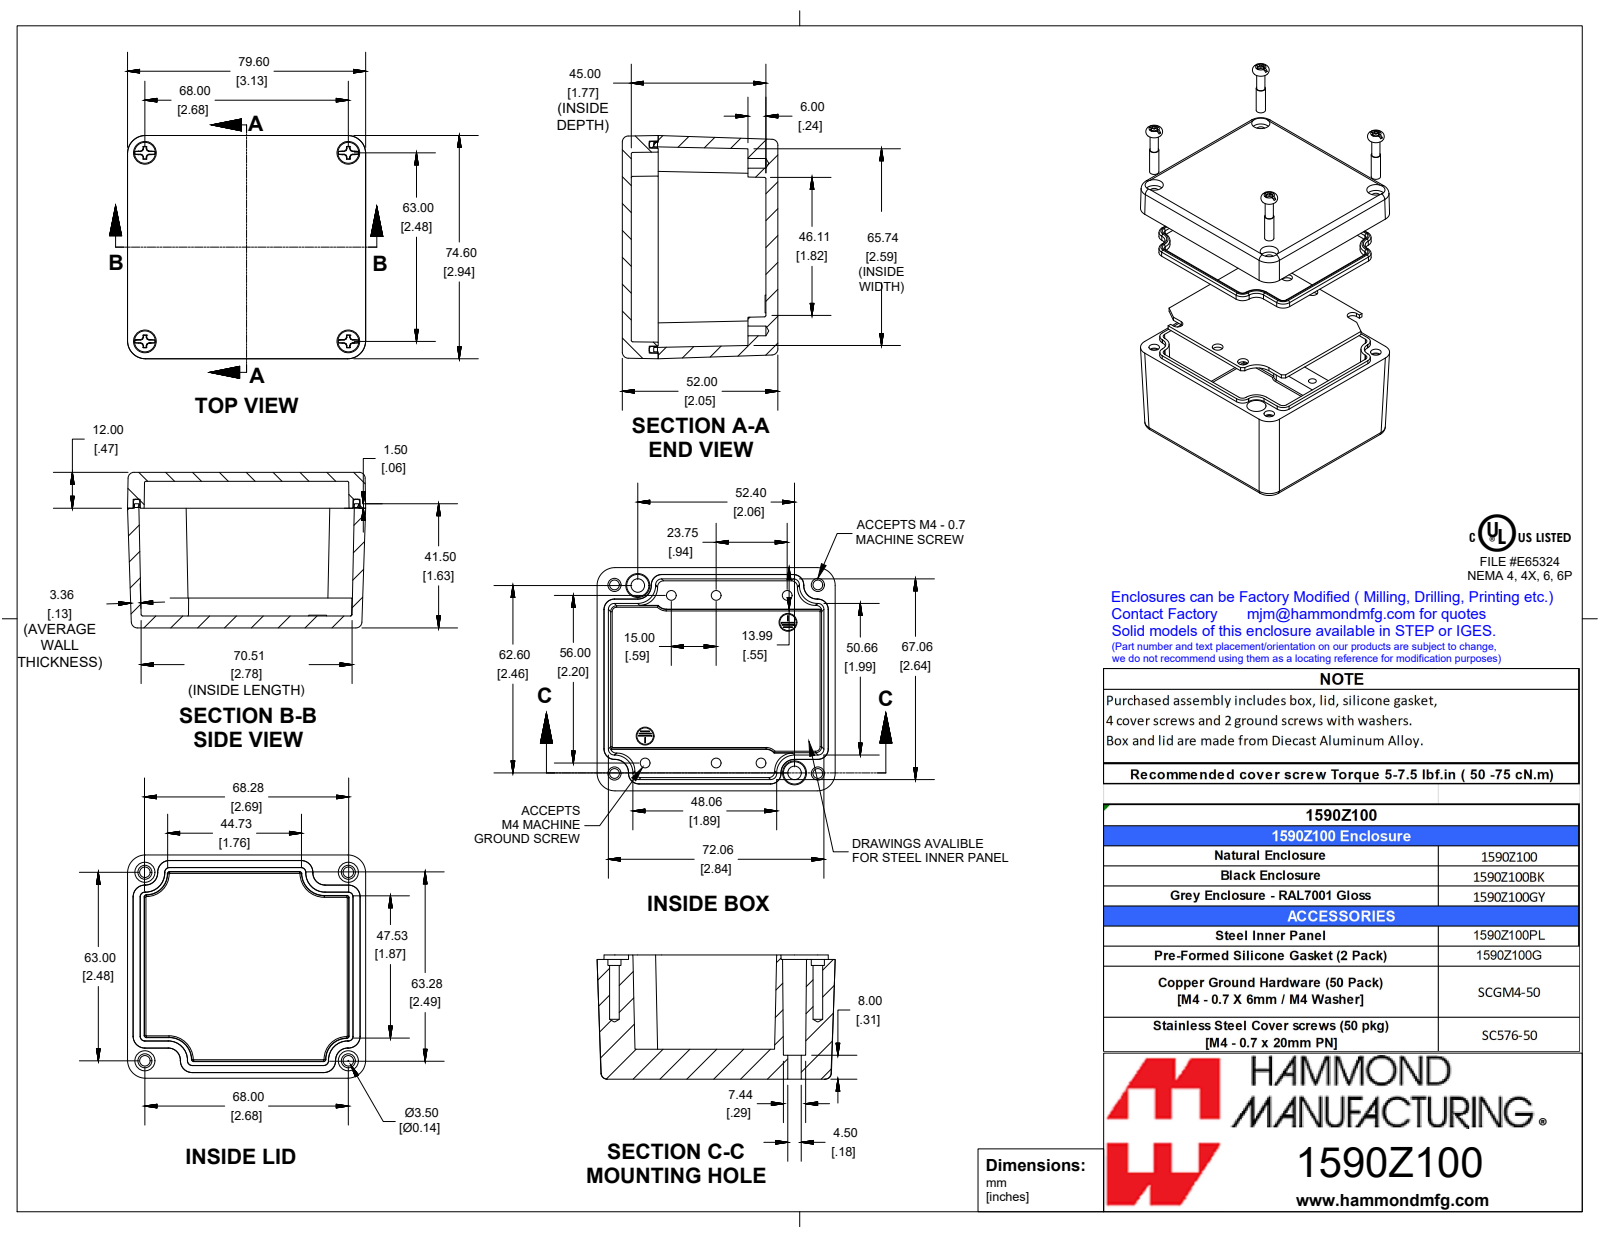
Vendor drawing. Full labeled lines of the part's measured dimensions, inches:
Part name (STEP PRODUCT): 1590Z100GY
STEP written by: SolidWorks 2019 (CONFIG_CONTROL_DESIGN)
Units: inches
Bodies: 8 solids, 515 faces (247 planar, 112 cylindrical, 156 other)
Overall size (bounding box): 3.134 × 2.937 × 2.047
Volume: 7.004 in³ · Surface area: 104.3 in²
Round holes (diameter × count): ⌀0.128 ×10, ⌀0.138 ×4, ⌀0.173 ×4, ⌀0.177 ×4, ⌀0.185 ×4, ⌀0.299 ×4, ⌀0.177 ×2, ⌀0.217 ×2
Round bosses / shafts (diameter × count): ⌀0.153 ×4, ⌀0.135 ×4, ⌀0.235 ×2
Partial cylindrical surfaces — rounded edges, fillets, slot ends (radius × count): R0.079 ×16, R0.02 ×12, R0.03 ×12, R0.236 ×12, R0.138 ×8, R0.177 ×4, R0.089 ×2, R0.28 ×2
Main face-to-face distances: 0.472, 1.575, 2.047, 0.118, 1.535, 0.394, 1.654, 1.929, 0.236, 0.079
Hole centre spacings: 1.346, 2.698, 0.307, 0.354, 0.426, 0.46, 0.591, 0.761
